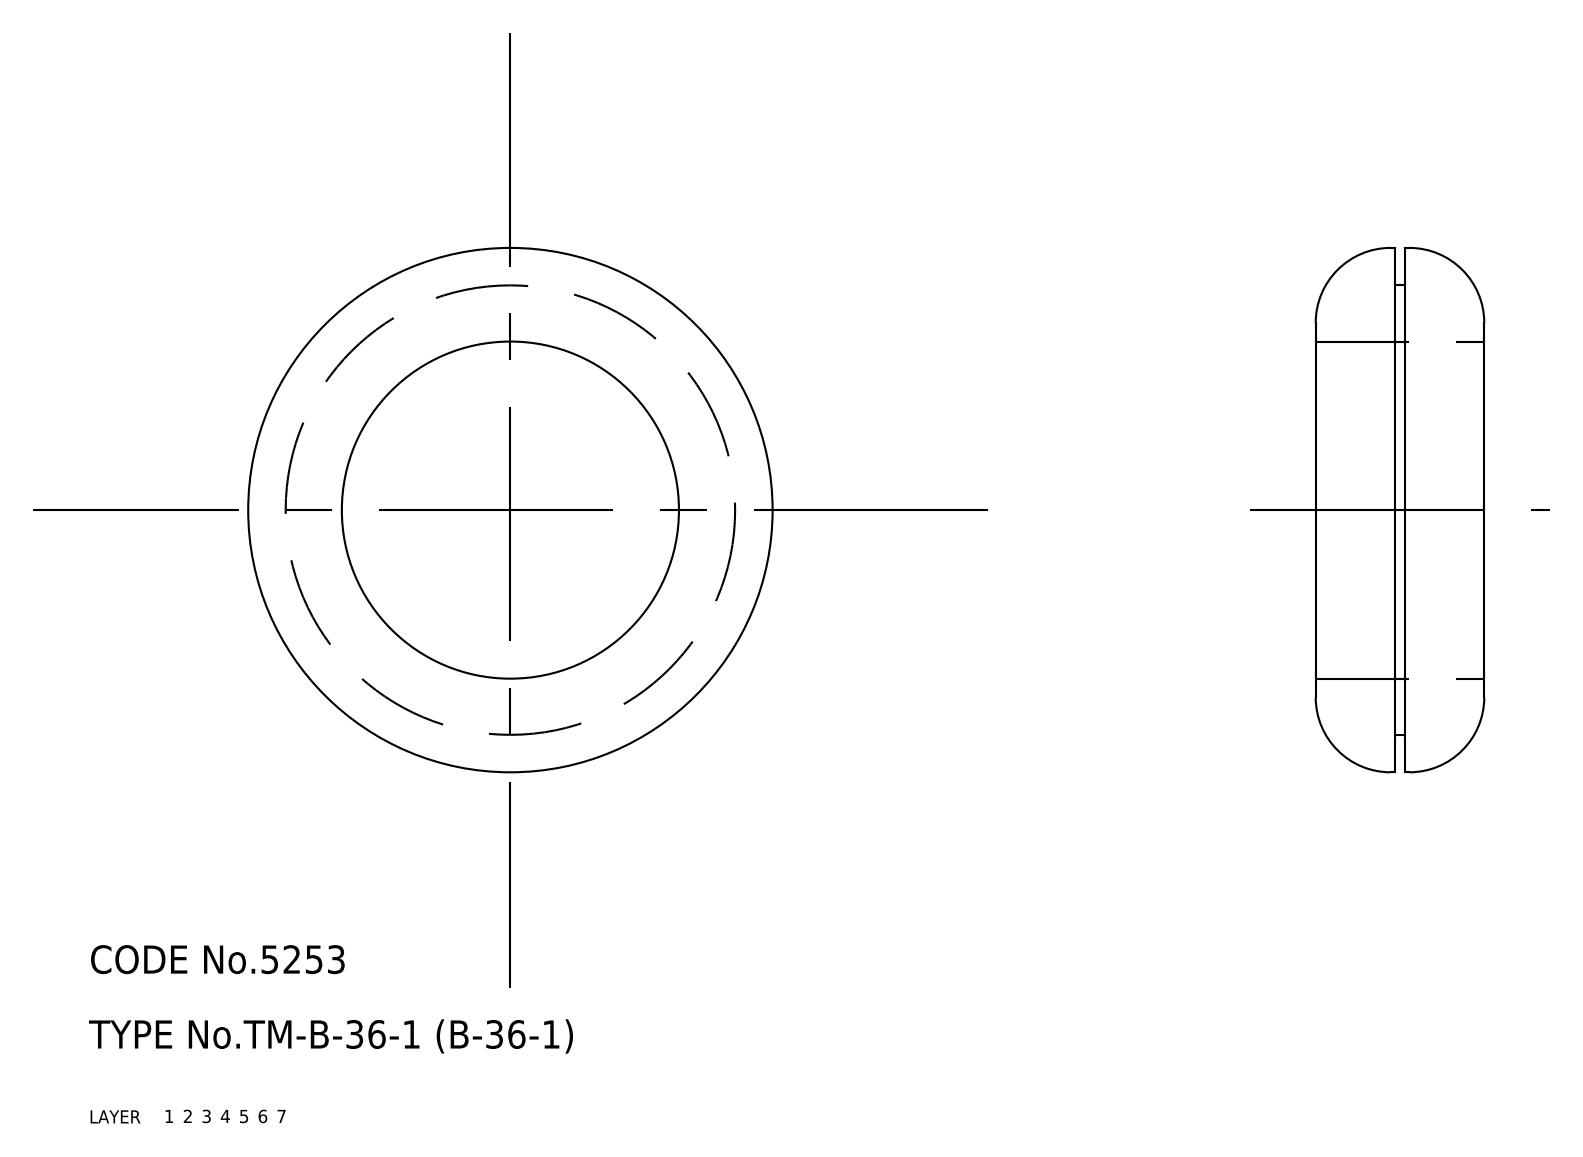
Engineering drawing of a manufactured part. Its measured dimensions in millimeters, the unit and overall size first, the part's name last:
Units: millimetres
Overall size (bounding box): 56 × 56 × 18
Volume: 20 892 mm³ · Surface area: 8 115 mm²
Bodies: 1 solid, 16 faces (0 planar, 0 cylindrical, 16 other)
Part name (STEP PRODUCT): grommet
STEP written by: CADfix (AUTOMOTIVE_DESIGN)
